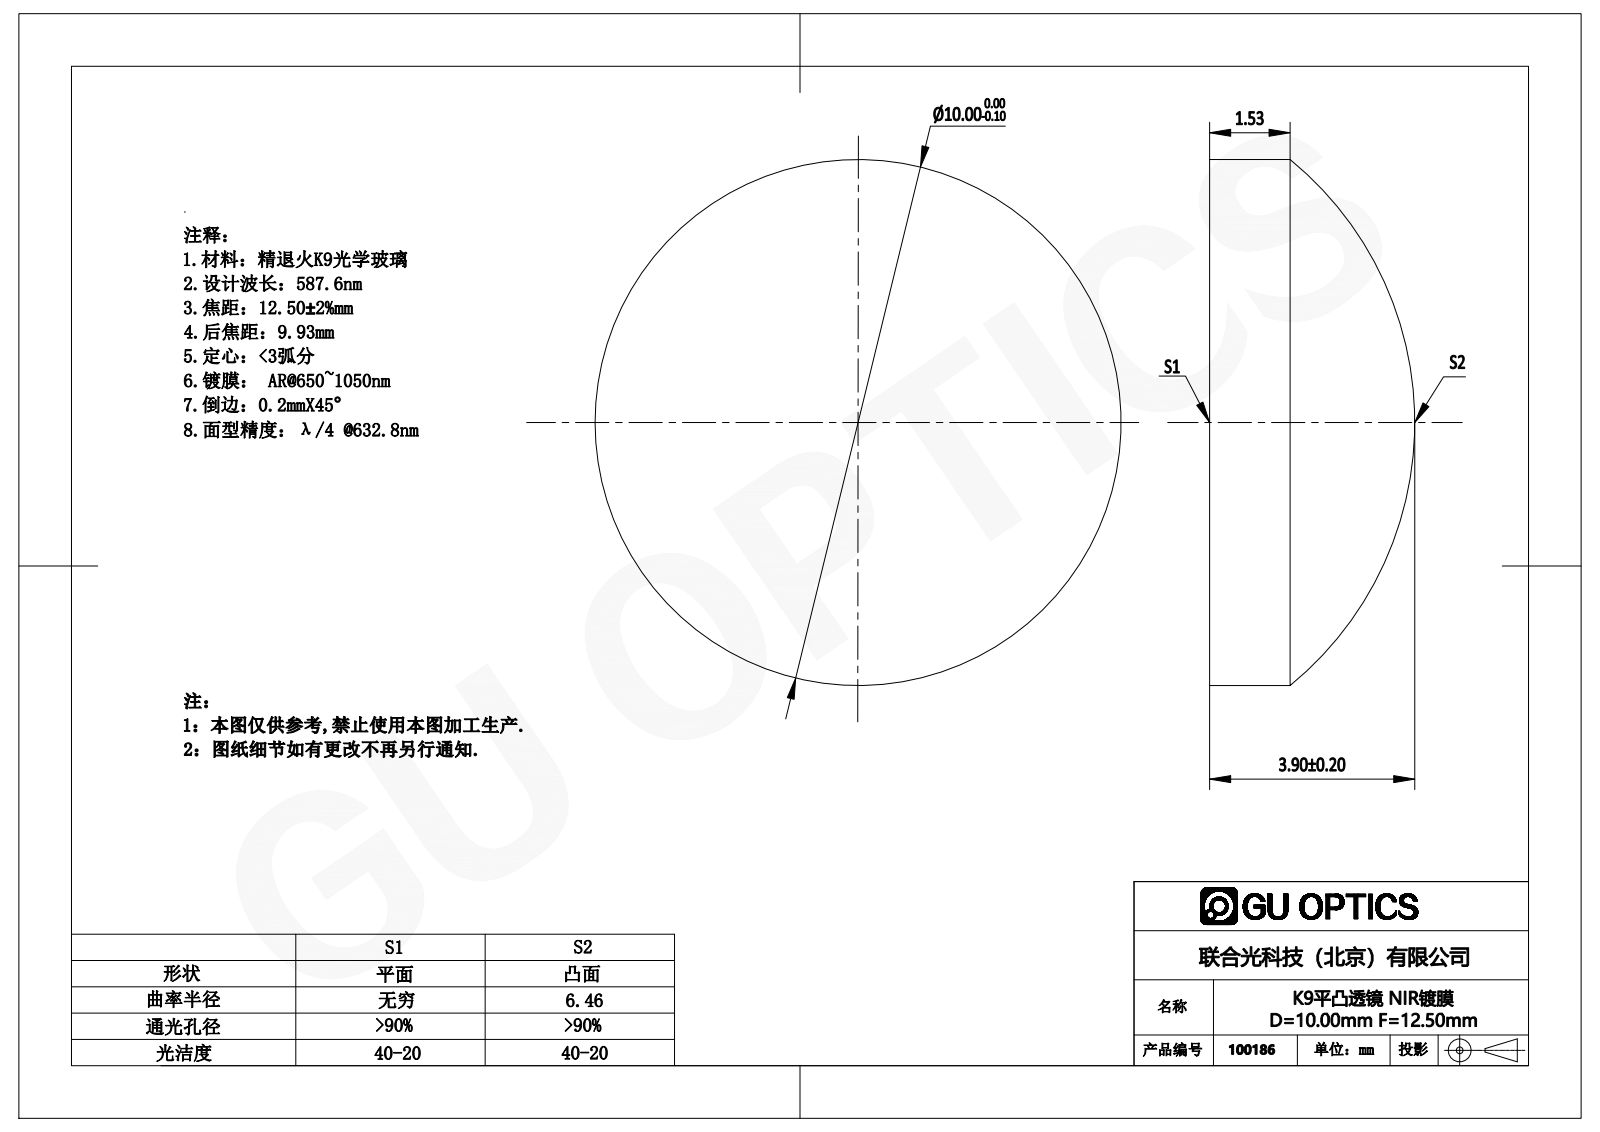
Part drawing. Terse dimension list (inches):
name: 100186
written by: SolidWorks 2016 (AUTOMOTIVE_DESIGN)
unit: in
bodies: 1 solid, 5 faces (1 planar, 2 cylindrical, 2 other)
size: 0.394 × 0.394 × 0.154
volume: 0.013 in³; area: 0.346 in²
bosses: 1× ⌀0.394
